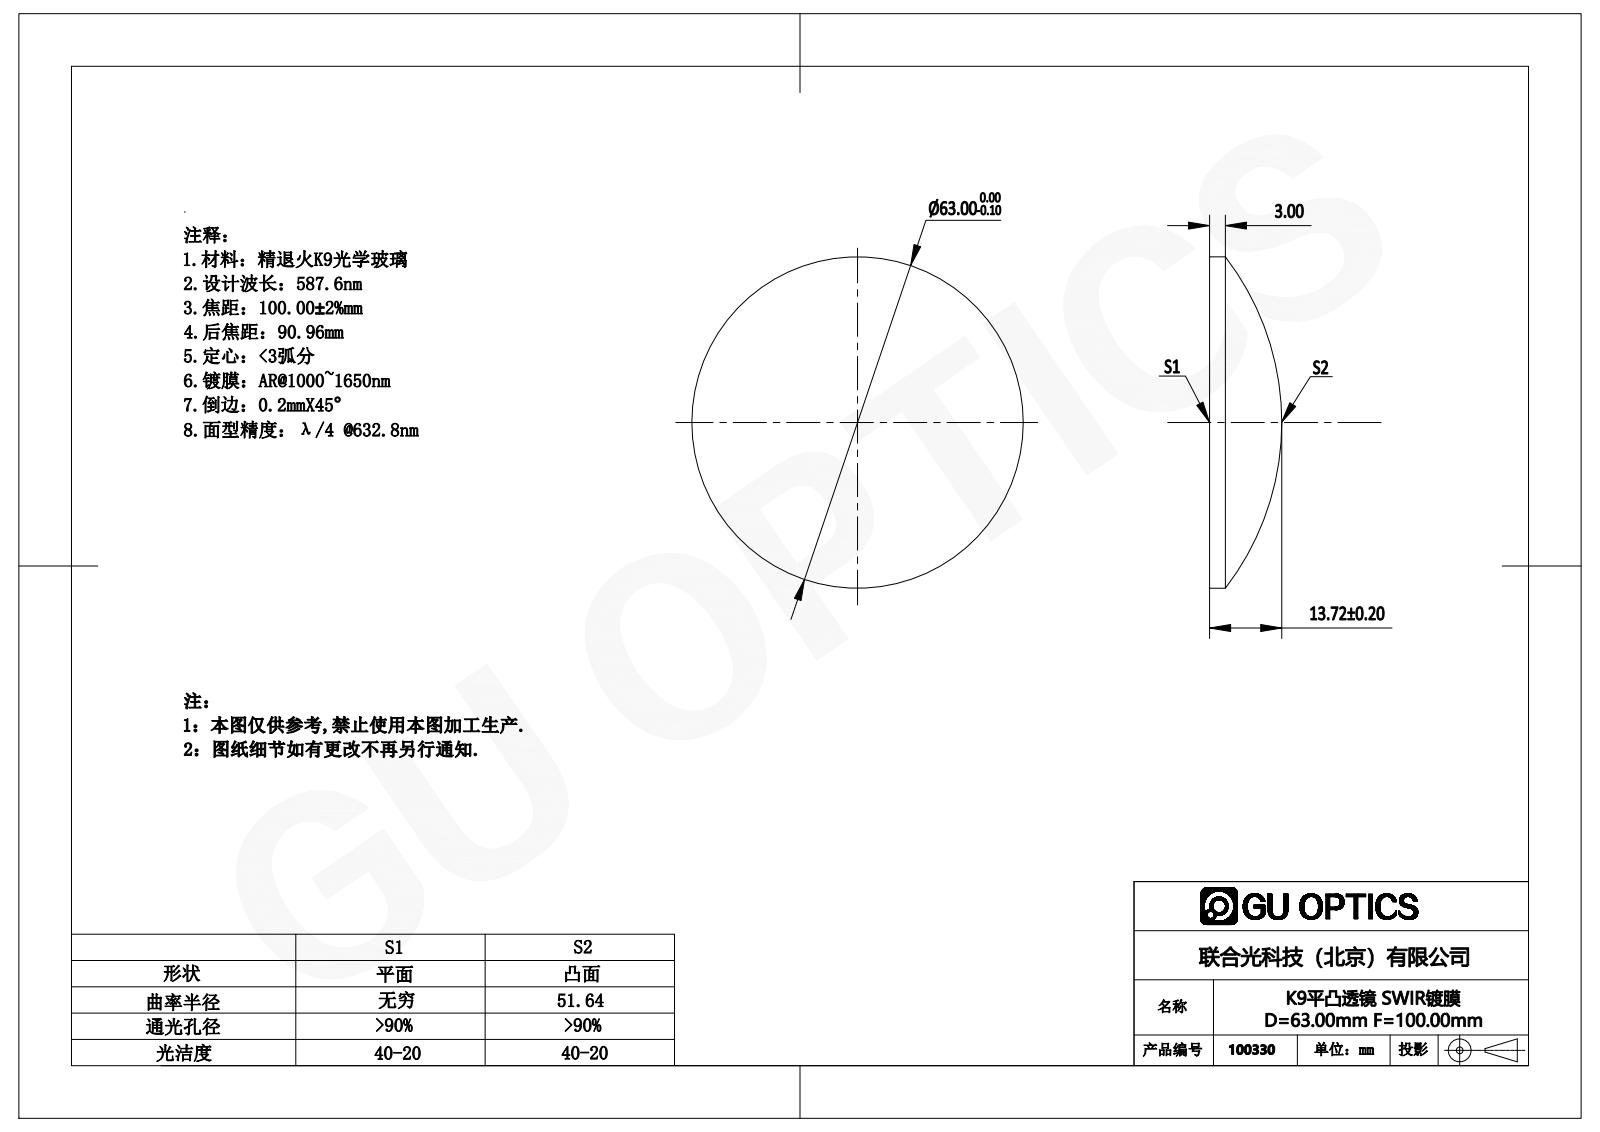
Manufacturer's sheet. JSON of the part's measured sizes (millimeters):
{"part_name": "100158", "step_written_by": "SolidWorks 2016 (AUTOMOTIVE_DESIGN)", "units": "millimeters", "bodies": {"solids": 1, "faces": 5, "planar": 1, "cylindrical": 2, "other": 2}, "overall_size": [63, 63, 13.72], "volume_mm3": 26705, "surface_area_mm2": 7189, "round_bosses_or_shafts": [[63, 1]]}
